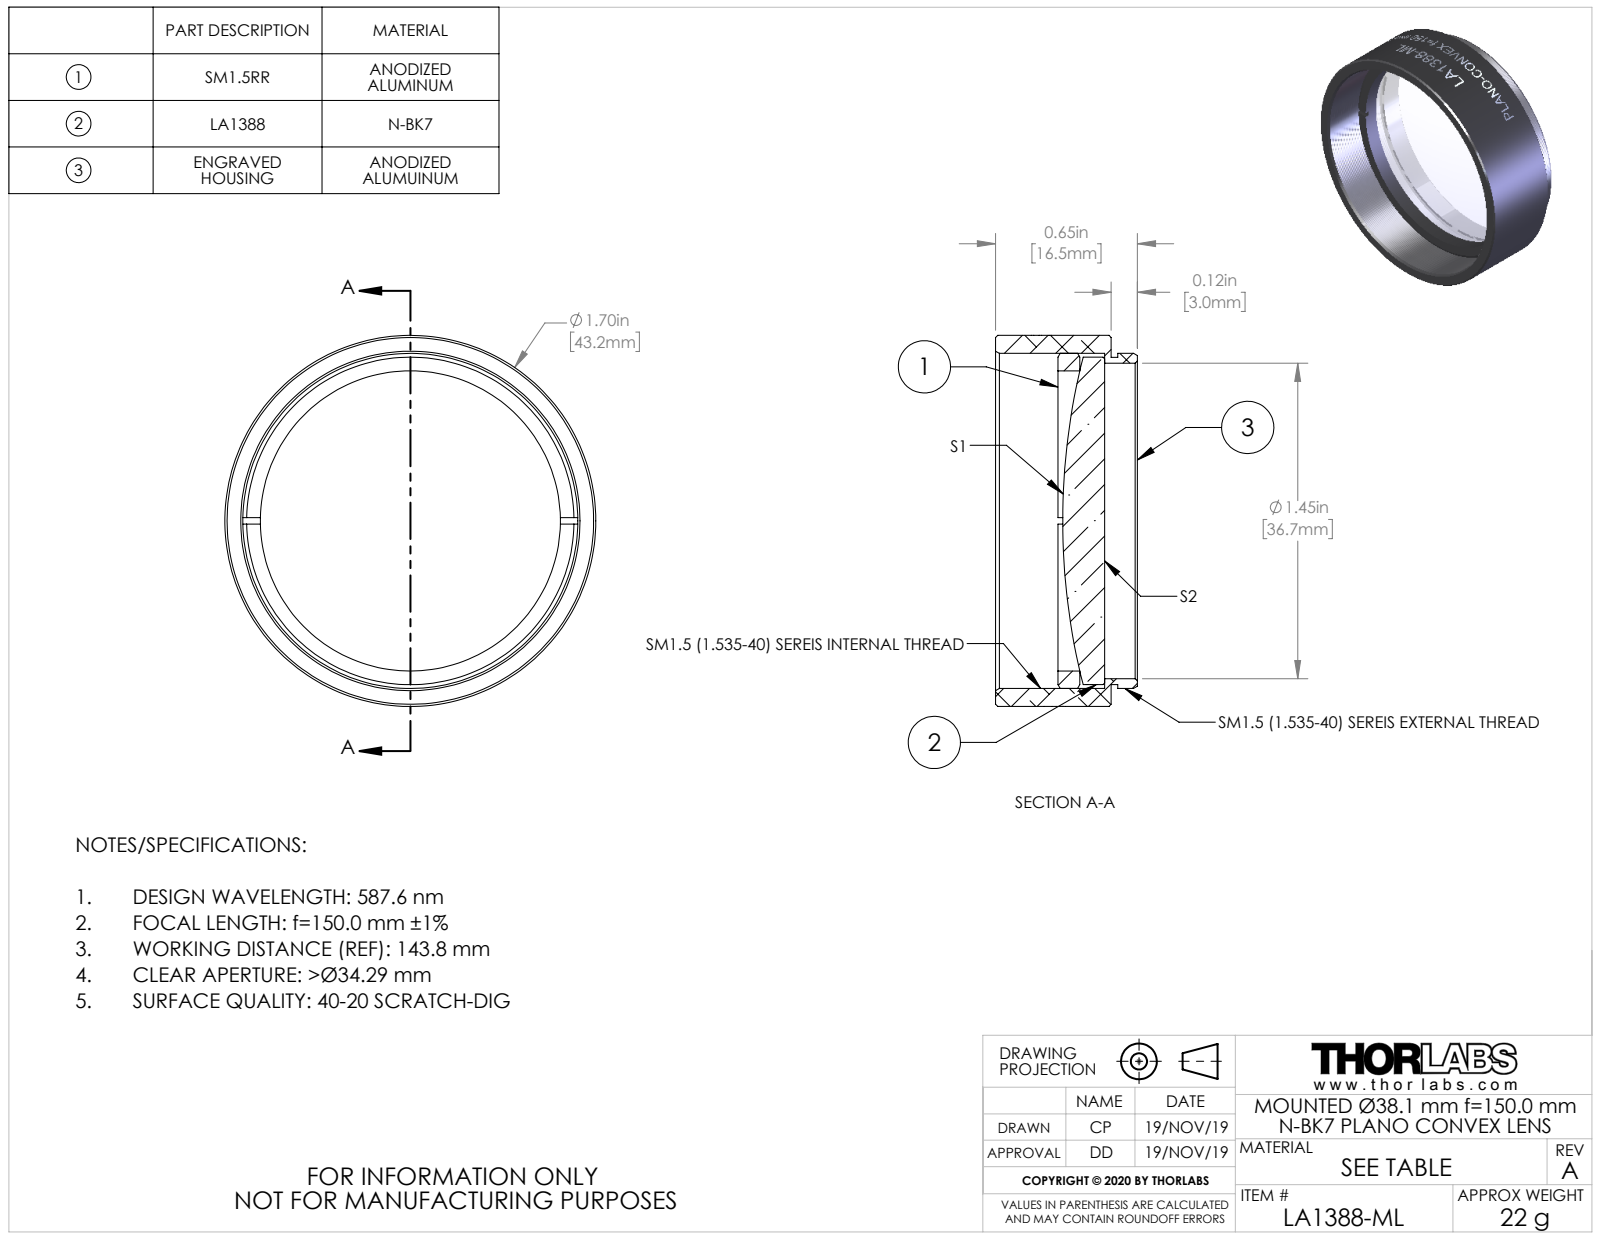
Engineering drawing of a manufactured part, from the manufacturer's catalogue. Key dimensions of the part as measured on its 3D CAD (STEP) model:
Part name (STEP PRODUCT): TTN200692-E0W
STEP written by: SolidWorks 2018 (CONFIG_CONTROL_DESIGN)
Units: millimetres
Bodies: 3 solids, 123 faces (15 planar, 89 cylindrical, 19 other)
Overall size (bounding box): 43.18 × 43.18 × 16.51
Volume: 8 887 mm³ · Surface area: 8 615 mm²
Round holes (diameter × count): ⌀34.92 ×1, ⌀36.7 ×1
Round bosses / shafts (diameter × count): ⌀43.18 ×1, ⌀38.99 ×1, ⌀38.1 ×1, ⌀38.07 ×1
Main face-to-face distances: 0.76, 13.46, 12.7, 3.65, 2.89, 9.81, 6.19, 5.43, 2.54, 7.27
